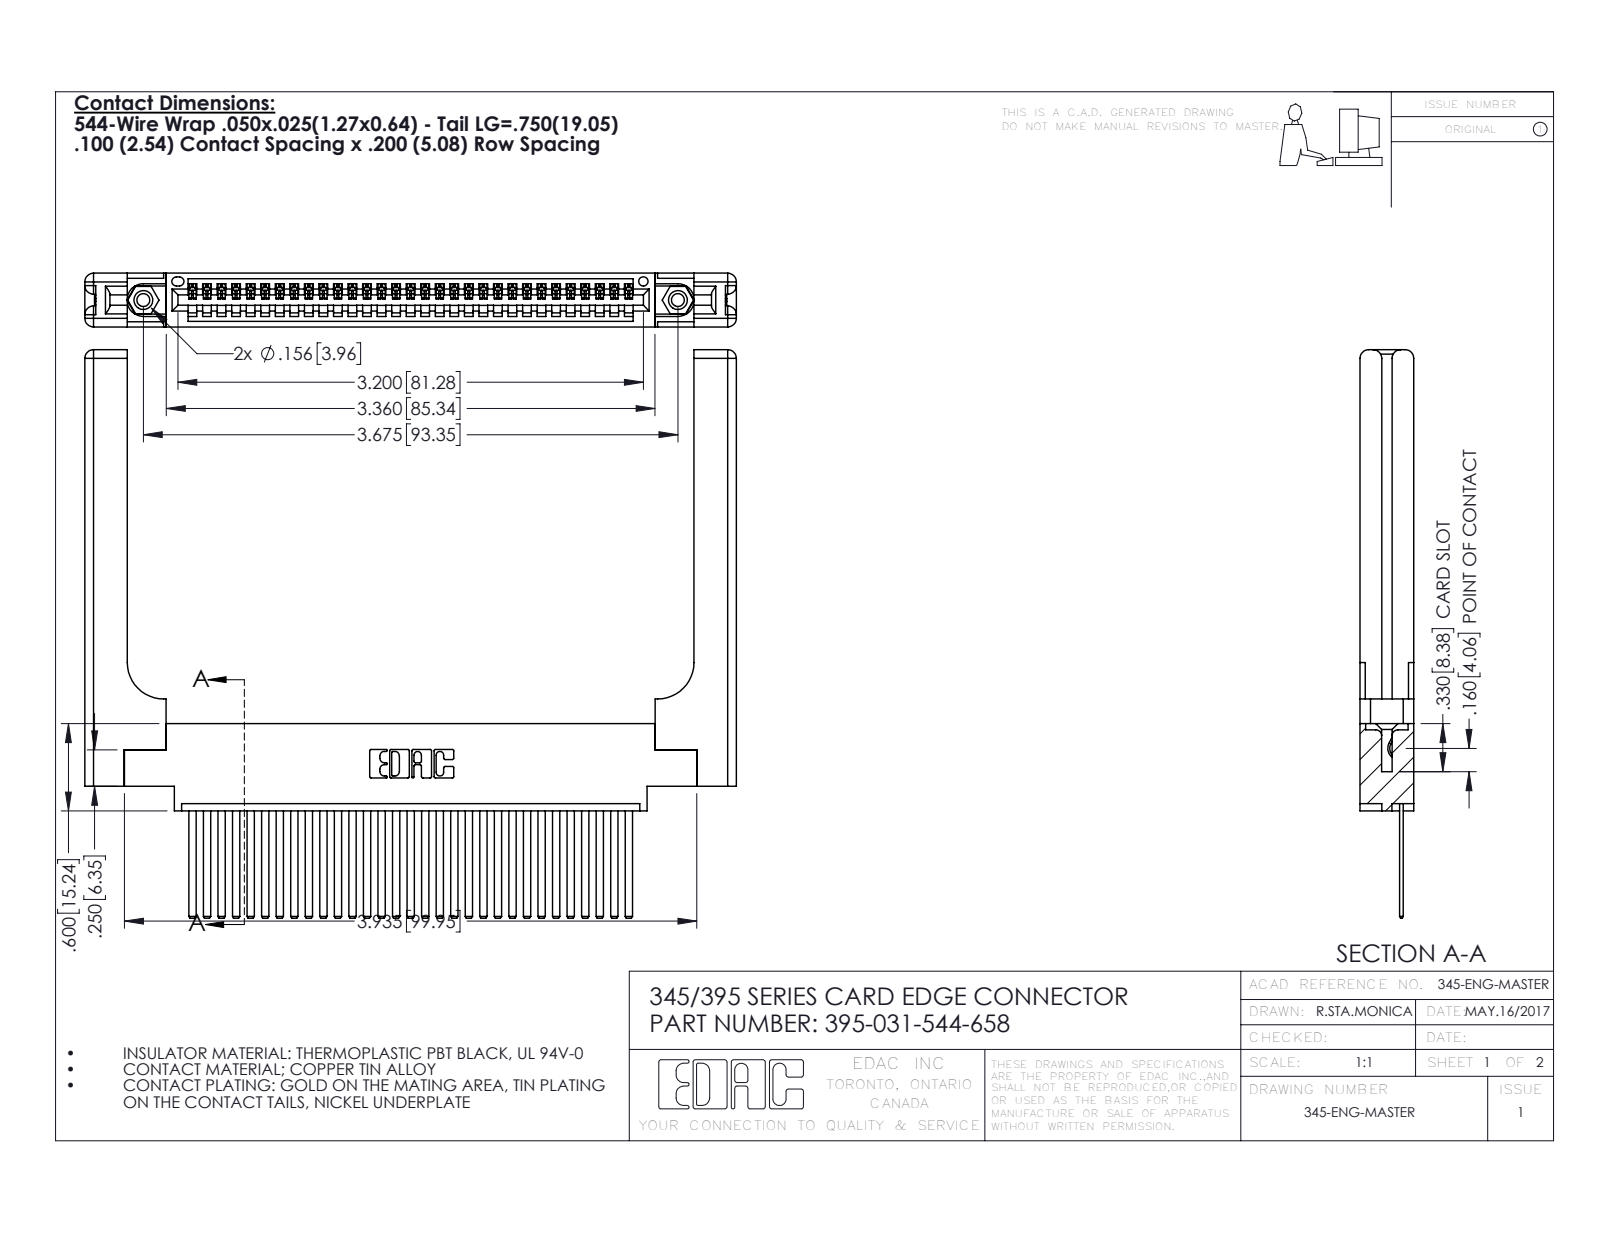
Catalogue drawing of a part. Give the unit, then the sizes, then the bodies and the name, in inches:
Units: inches
Overall size (bounding box): 4.479 × 3.907 × 0.37
Round holes (diameter × count): ⌀0.089 ×2, ⌀0.125 ×2, ⌀0.156 ×2, ⌀0.064 ×1
Round bosses / shafts (diameter × count): ⌀0.155 ×2
Partial cylindrical surfaces — rounded edges, fillets, slot ends (radius × count): R0.006 ×62, R0.01 ×22, R0.06 ×16, R0.007 ×6, R0.031 ×6, R0.026 ×3, R0.03 ×2, R0.031 ×2
Main face-to-face distances: 0.072, 0.37, 0.298, 0.098, 0.272, 0.025, 0.2, 0.148, 0.15, 0.077
Hole centre spacings: 0.27, 3.44, 3.675
Volume: 1.188 in³ · Surface area: 32.44 in²
Bodies: 36 solids, 1998 faces (1348 planar, 590 cylindrical, 60 other)
Part name (STEP PRODUCT): 345-292-001_345-293-144; 345 Part_0.170 Offset - 0.156 Dia-TH; 395-031-544-658; 345-220-058_345-220-058 (+1 more)
STEP written by: SolidWorks 2016 (CONFIG_CONTROL_DESIGN)
